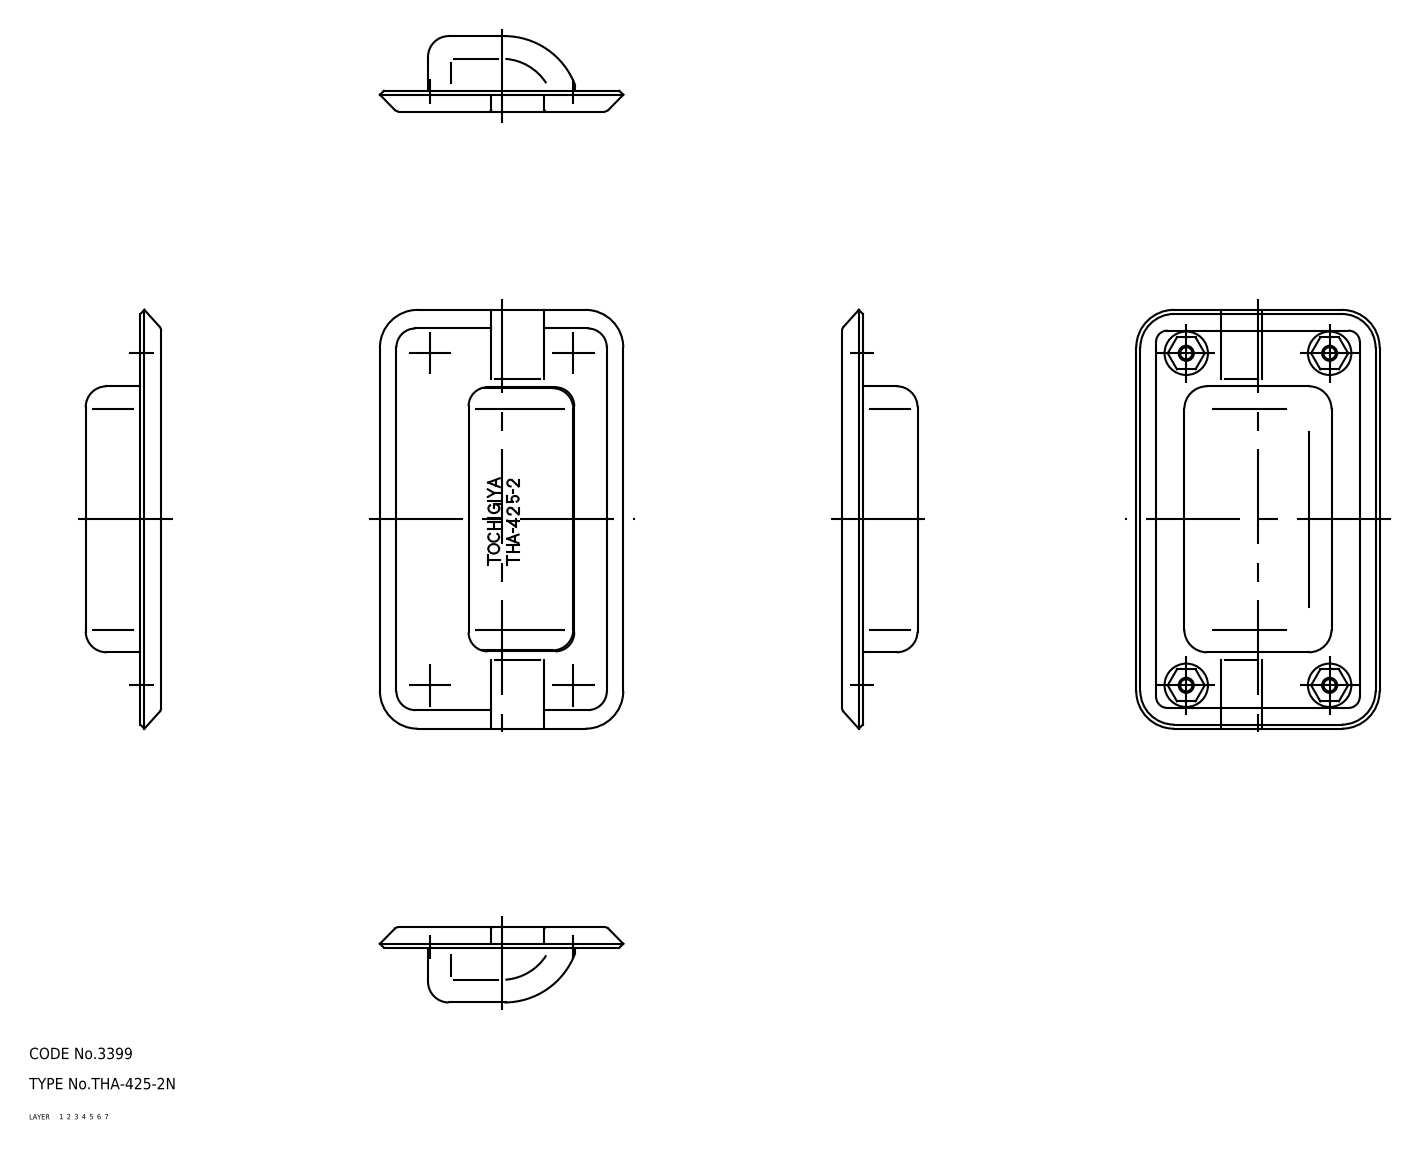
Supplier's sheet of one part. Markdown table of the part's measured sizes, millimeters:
| quantity | value |
| --- | --- |
| part name | nut; cover; base; THA_425_2N_28836_36 |
| STEP written by | CADfix (AUTOMOTIVE_DESIGN) |
| units | millimeters |
| bodies | 6 solids, 465 faces (0 planar, 0 cylindrical, 465 other) |
| overall size | 111 × 64.5 × 20 |
| volume | 13 117 mm³ |
| surface area | 29 479 mm² |
